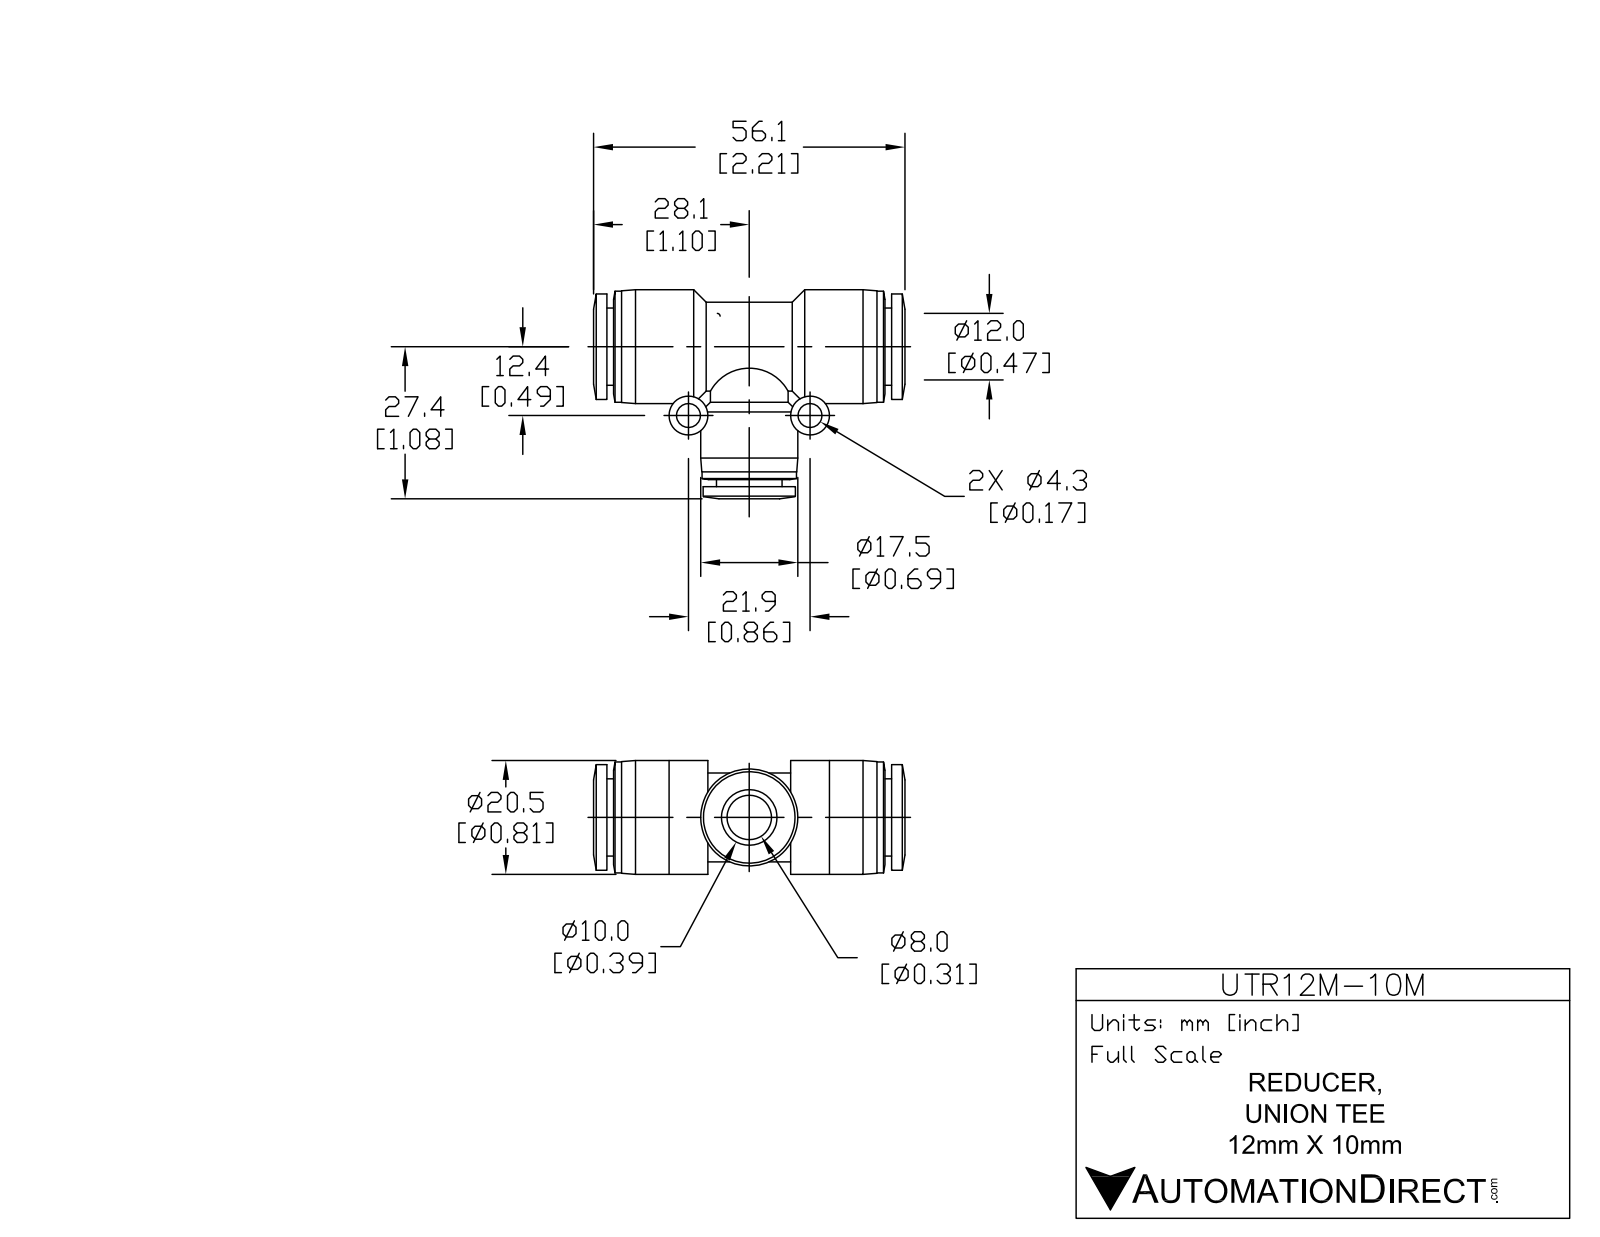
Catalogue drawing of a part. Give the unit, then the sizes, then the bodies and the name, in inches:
Units: inches
Overall size (bounding box): 2.209 × 1.482 × 0.807
Round holes (diameter × count): ⌀0.169 ×2, ⌀0.315 ×2, ⌀0.406 ×1, ⌀0.484 ×1
Round bosses / shafts (diameter × count): ⌀0.276 ×2, ⌀0.807 ×1, ⌀0.787 ×1, ⌀0.748 ×1, ⌀0.689 ×1, ⌀0.669 ×1, ⌀0.654 ×1, ⌀0.63 ×1
Main face-to-face distances: 0.807, 0.047, 1.972, 1.213, 0.76, 1.165, 2.02, 1.925, 0.406, 0.049
Hole centre spacings: 0.862
Volume: 0.775 in³ · Surface area: 14.94 in²
Bodies: 1 solid, 97 faces (19 planar, 46 cylindrical, 32 other)
Part name (STEP PRODUCT): UTR12M-10M
STEP written by: SolidWorks 2015 (AUTOMOTIVE_DESIGN)
